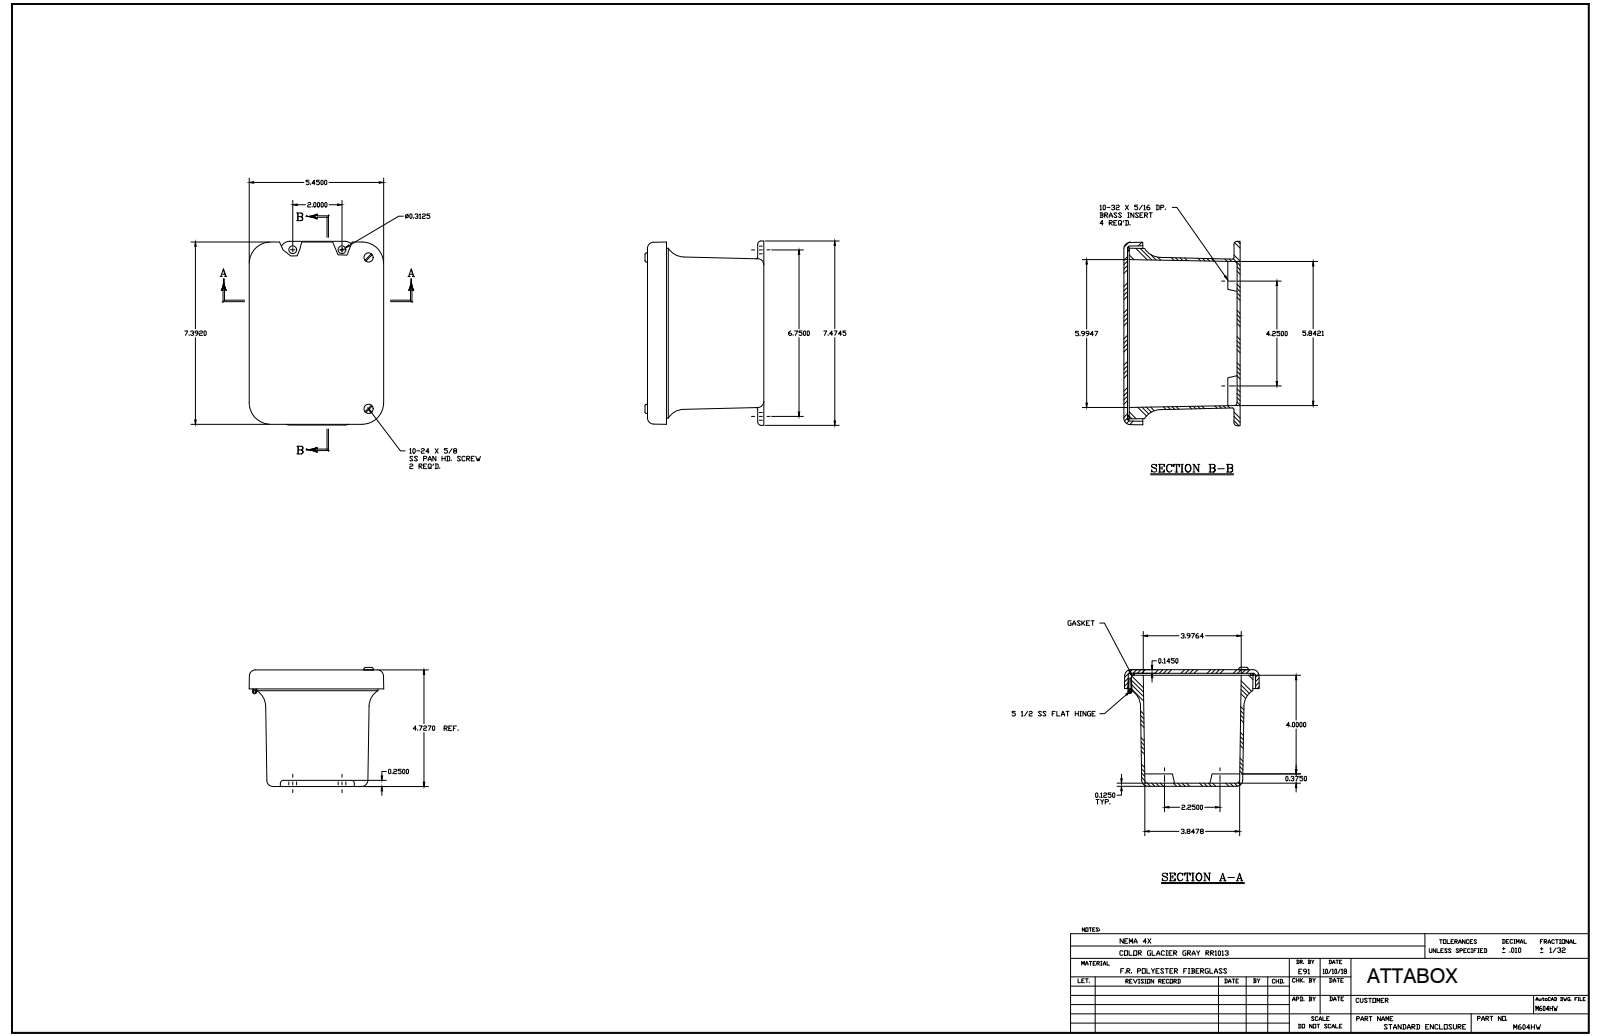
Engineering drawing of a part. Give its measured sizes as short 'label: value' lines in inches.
name: M604HW
written by: SolidWorks 2018 (AUTOMOTIVE_DESIGN)
unit: in
bodies: 19 solids, 653 faces (200 planar, 247 cylindrical, 206 other)
size: 7.474 × 5.484 × 4.848
volume: 31.29 in³; area: 393.1 in²
holes: 5× ⌀0.131, 5× ⌀0.14, 5× ⌀0.152, 4× ⌀0.156, 4× ⌀0.218, 2× ⌀0.145, 1× ⌀0.085, 1× ⌀0.085
bosses: 6× ⌀0.27, 5× ⌀0.25, 5× ⌀0.125, 2× ⌀0.19, 2× ⌀0.156, 1× ⌀0.155
rounds: 20× R0.031, 12× R0.125, 8× R0.25, 6× R0.2, 4× R0.375, 4× R0.75, 2× R0.063
face distances: 0.145, 4.572, 4.717, 0.125, 4.447, 4.592, 4.5, 0.217, 4.375, 0.072
hole spacings: 2.5, 3.339, 0.5, 1.341, 2, 2.25, 4, 4.156
